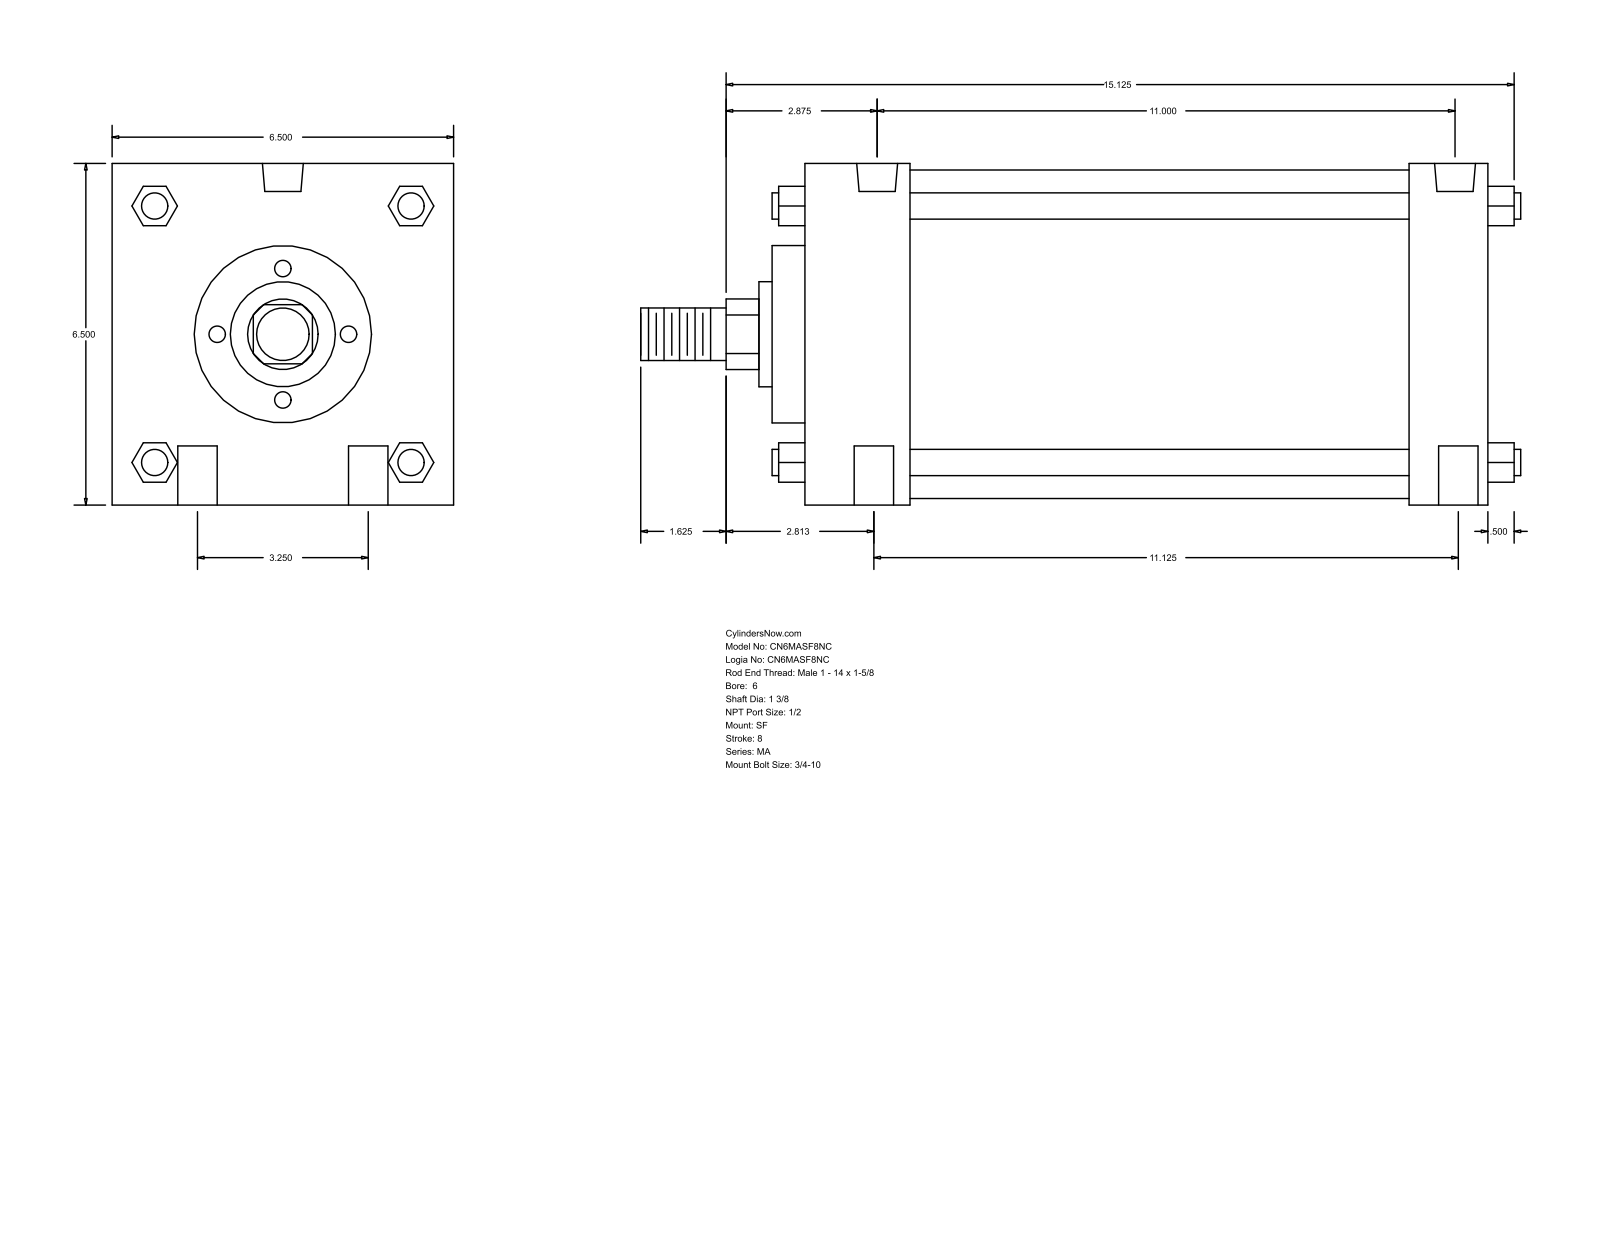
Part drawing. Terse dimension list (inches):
name: MA_SF__0600_1.375
written by: GSSL Pune (CONFIG_CONTROL_DESIGN)
unit: in
bodies: 0 solids, 126 faces (95 planar, 31 cylindrical, 0 other)
size: 16.75 × 6.5 × 6.5
holes: 4× ⌀0.75, 2× ⌀0.687, 2× ⌀0.778
bosses: 4× ⌀0.5, 1× ⌀6.25, 1× ⌀3.375, 1× ⌀2, 1× ⌀1.375, 1× ⌀1
rounds: 1× R0.672
face distances: 6.5, 13, 11.5, 2, 1.5, 9.5, 11, 2.625, 0.625, 12.125
hole spacings: 1.626, 3.25, 11, 11.125, 11.181, 11.181, 11.59
